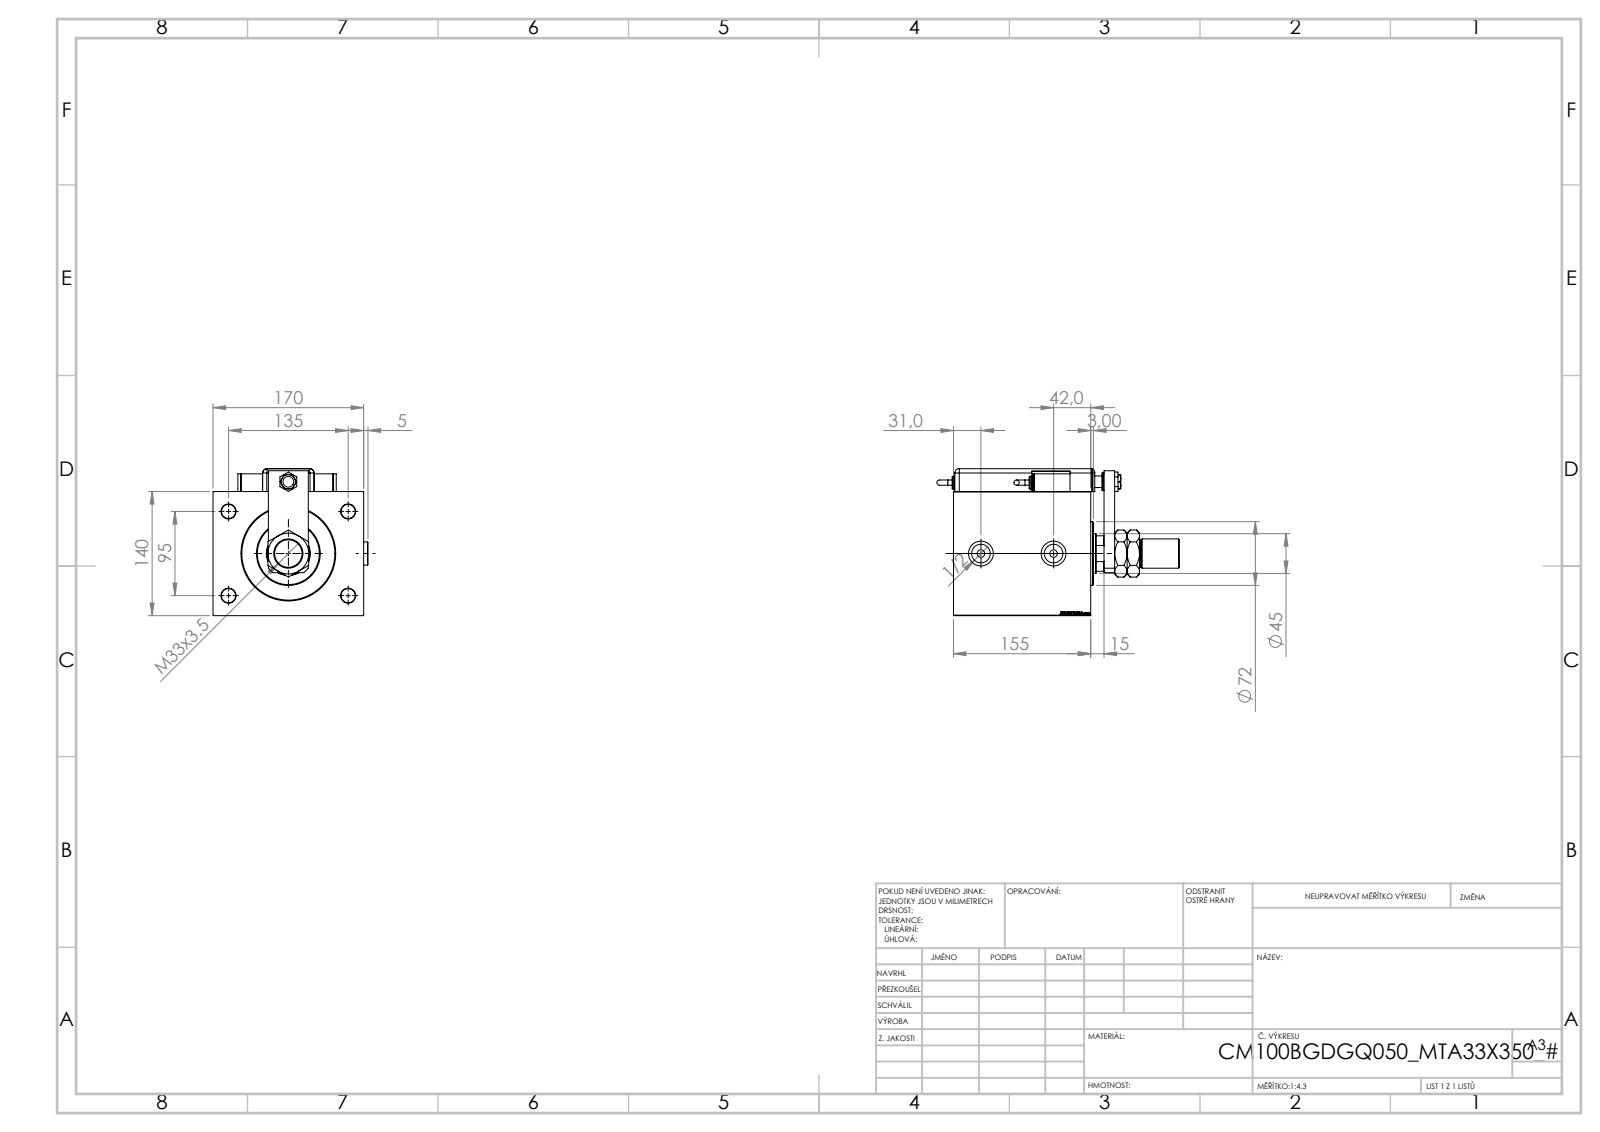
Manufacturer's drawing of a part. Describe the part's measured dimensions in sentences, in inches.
The part is named "KRYT; SWITCH DIM A_G; SWITCH Q; NUT_D19 (+7 more)". Its 3-D file was written by "SolidWorks 2019 (CONFIG_CONTROL_DESIGN)". It is 16 solids with 1371 faces: 657 planar, 131 cylindrical and 583 other. Overall it measures 10.778 by 6.886 by 6.528 inches. Its volume is 219.4 cubic inches and its surface area 567.8 square inches. Round holes: 4 of diameter 0.63, 2 of diameter 0.157, 2 of diameter 0.315, 2 of diameter 0.335, 2 of diameter 0.825, 2 of diameter 1.102, 1 of diameter 0.472, 1 of diameter 0.512, 1 of diameter 0.551, 1 of diameter 1.24, 1 of diameter 1.299, 1 of diameter 1.772. Round bosses or shafts: 3 of diameter 0.787, 2 of diameter 1.024, 2 of diameter 0.63, 2 of diameter 0.551, 2 of diameter 0.236, 1 of diameter 2.835, 1 of diameter 1.22. Partial cylindrical surfaces (rounded edges, fillets, slot ends): 9 of radius 0.197, 1 of radius 0.394, 1 of radius 0.866. The main face-to-face distances are 5.512, 6.693, 6.102, 0.118, 1.024, 5.079, 0.591, 4.488, 0.059, 1.016. The hole center spacings are 3.25, 2.967, 3.74, 5.315, 5.715, 6.499, 0.787, 3.189.
